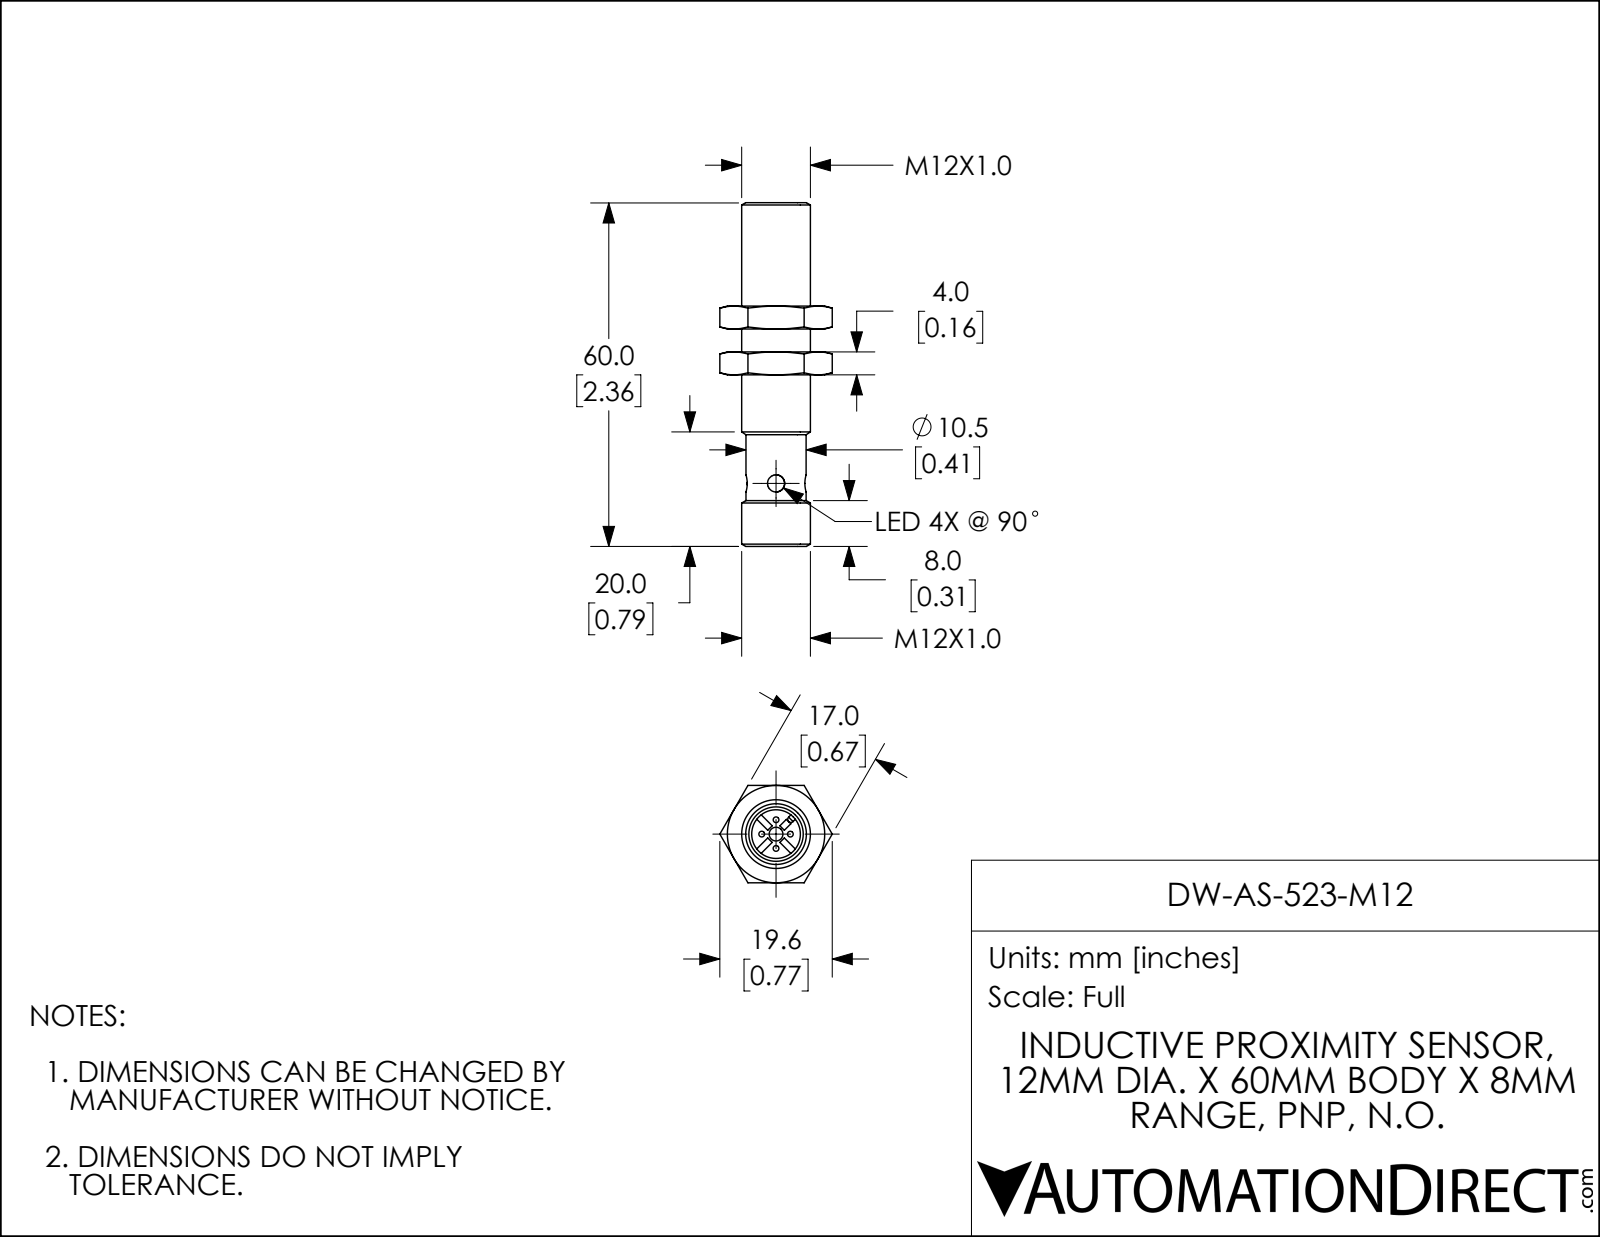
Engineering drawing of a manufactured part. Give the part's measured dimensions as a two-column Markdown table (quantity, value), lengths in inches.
| quantity | value |
| --- | --- |
| part name | DW-AS-523-M12 |
| STEP written by | SolidWorks 2018 (AUTOMOTIVE_DESIGN) |
| units | inches |
| bodies | 3 solids, 104 faces (46 planar, 19 cylindrical, 39 other) |
| overall size | 2.362 × 0.773 × 0.669 |
| volume | 0.439 in³ |
| surface area | 6.386 in² |
| round holes (diameter × count) | 0.118 × 2, 0.094 × 1, 0.335 × 1, 0.415 × 1, 0.43 × 1 |
| round bosses / shafts (diameter × count) | 0.039 × 4, 0.472 × 1, 0.413 × 1, 0.406 × 1 |
| partial cylindrical surfaces (radius × count) | 0.022 × 2 |
| main face-to-face distances | 0.157, 0.315, 0.669, 0.472, 1.183, 1.026, 0.868, 0.711, 0.837, 0.994 |
